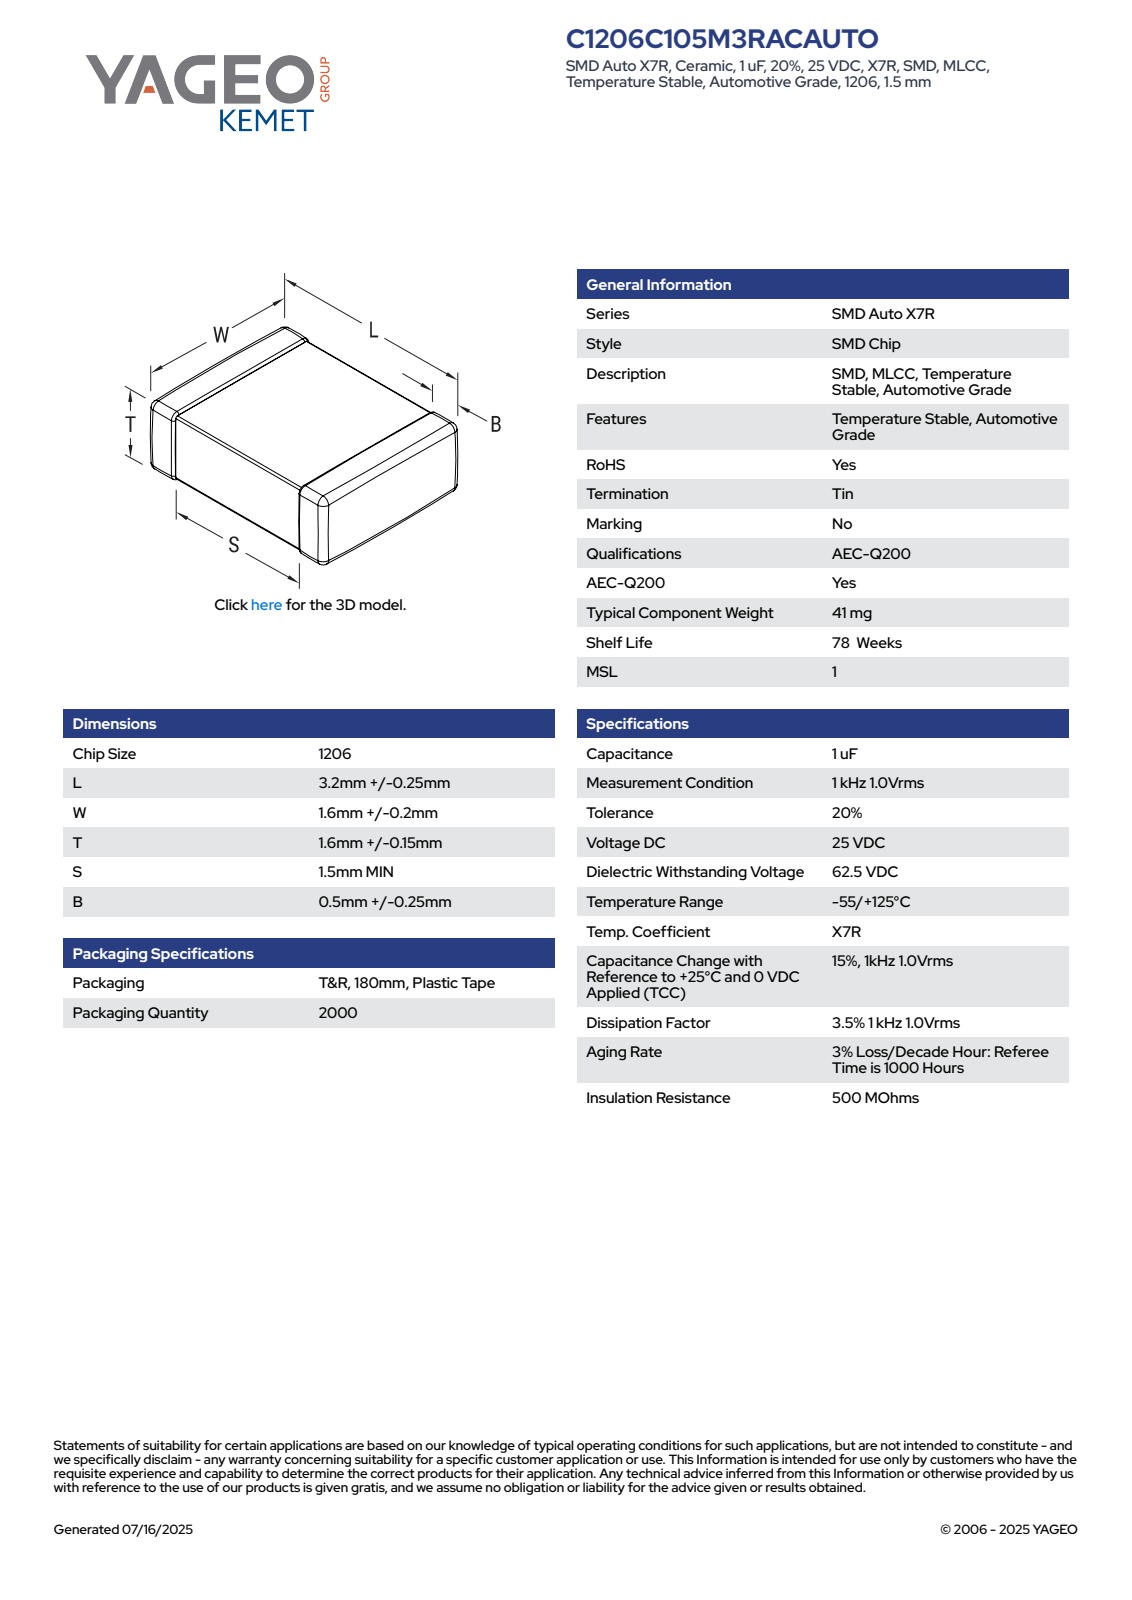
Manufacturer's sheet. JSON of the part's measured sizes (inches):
{"part_name": "CCS_CCSTD_1206_L3.45W1.8T1.75B0.5", "step_written_by": "SolidWorks 2021 (AUTOMOTIVE_DESIGN)", "units": "inches", "bodies": {"solids": 4, "faces": 125, "planar": 71, "cylindrical": 38, "other": 16}, "overall_size": [0.136, 0.071, 0.069], "volume_in3": 0.001, "surface_area_in2": 0.048, "face_to_face_distances": [0.067, 0.069, 0.068, 0.066, 0.136, 0.069, 0.071, 0.066, 0.063, 0.073]}
